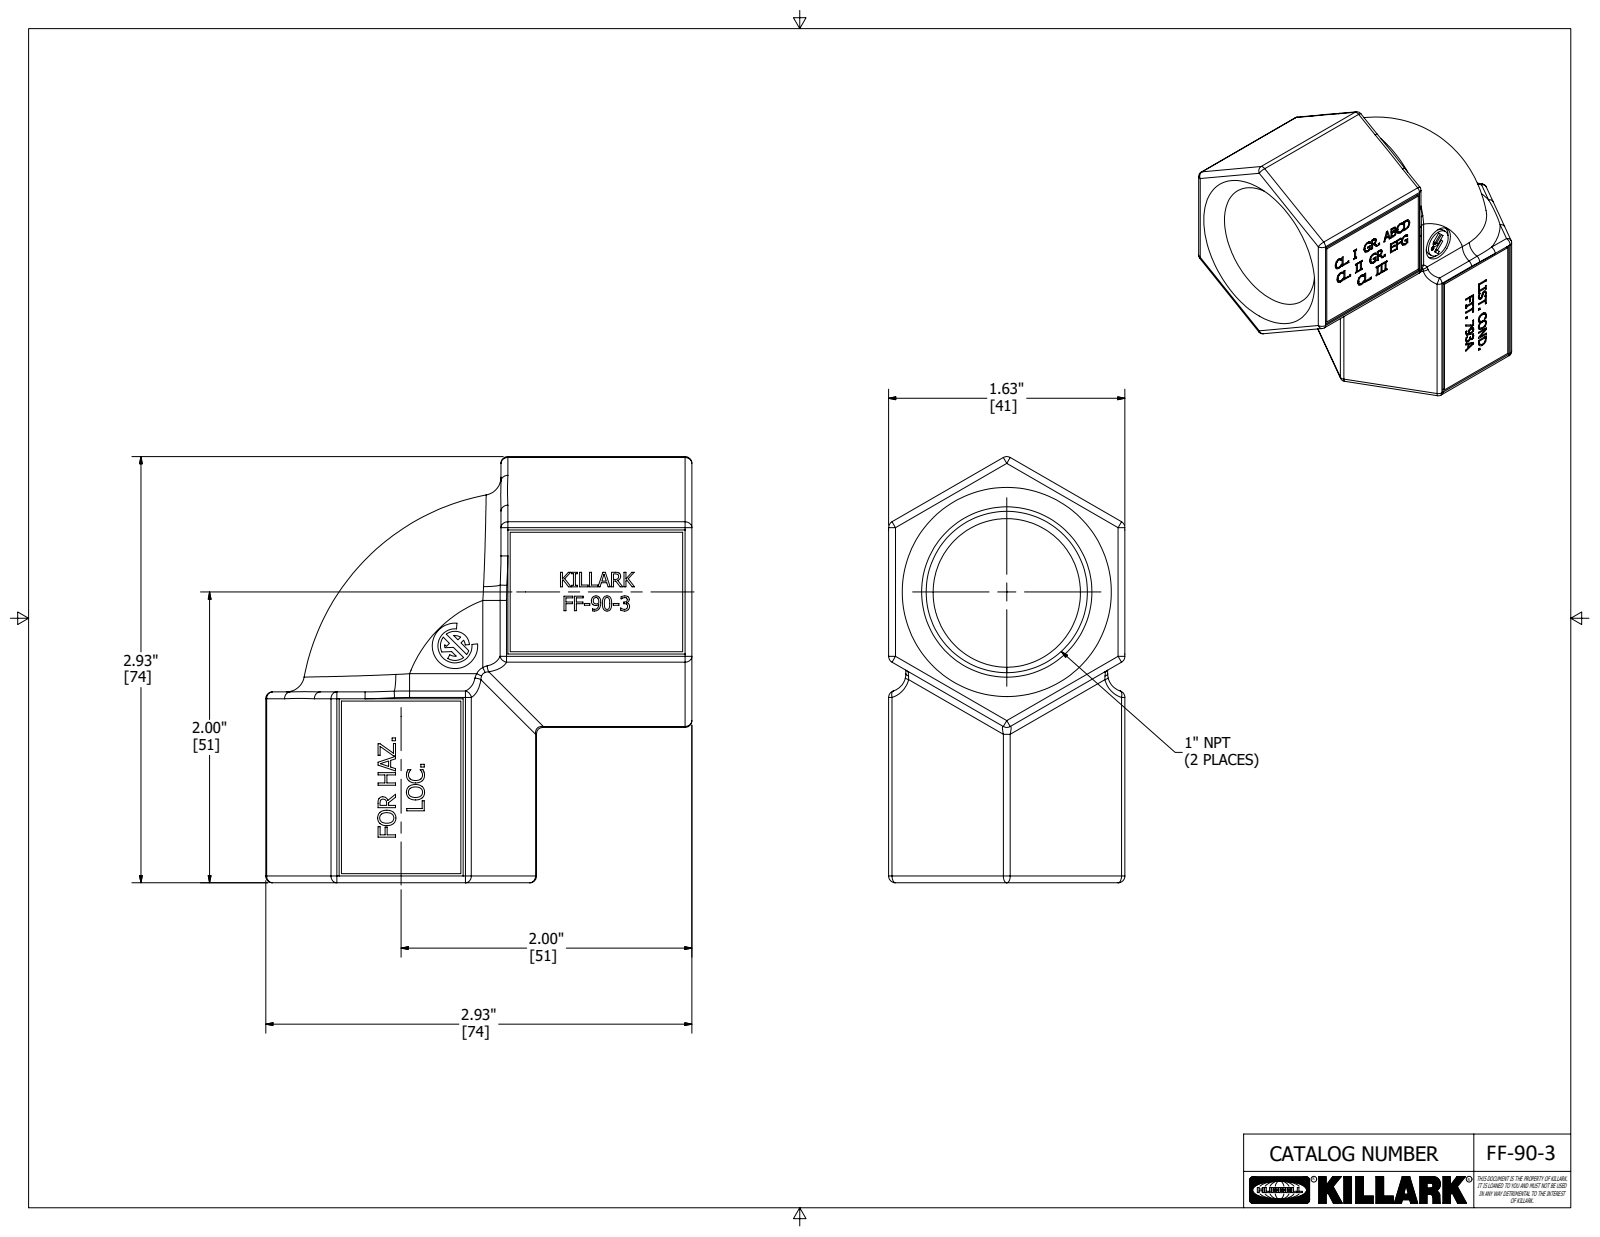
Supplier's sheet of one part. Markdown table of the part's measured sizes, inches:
| quantity | value |
| --- | --- |
| part name | FF-90-3 |
| STEP written by | Autodesk Inventor 2020 (AUTOMOTIVE_DESIGN) |
| units | inches |
| bodies | 1 solid, 1189 faces (722 planar, 64 cylindrical, 403 other) |
| overall size | 2.93 × 2.93 × 1.625 |
| volume | 4.009 in³ |
| surface area | 35.72 in² |
| round holes (diameter × count) | 0.035 × 1, 0.313 × 1 |
| round bosses / shafts (diameter × count) | 0.255 × 1, 0.029 × 1 |
| partial cylindrical surfaces (radius × count) | 0.047 × 36, 0.125 × 4, 0.062 × 2, 0.005 × 1, 0.01 × 1, 0.039 × 1, 0.071 × 1, 0.1 × 1 |
| main face-to-face distances | 1.625, 0.031, 1.594, 0.016, 0.119, 1.475, 0.087, 1.507, 2.363, 1.16 |
| hole center spacings | 0.076 |
